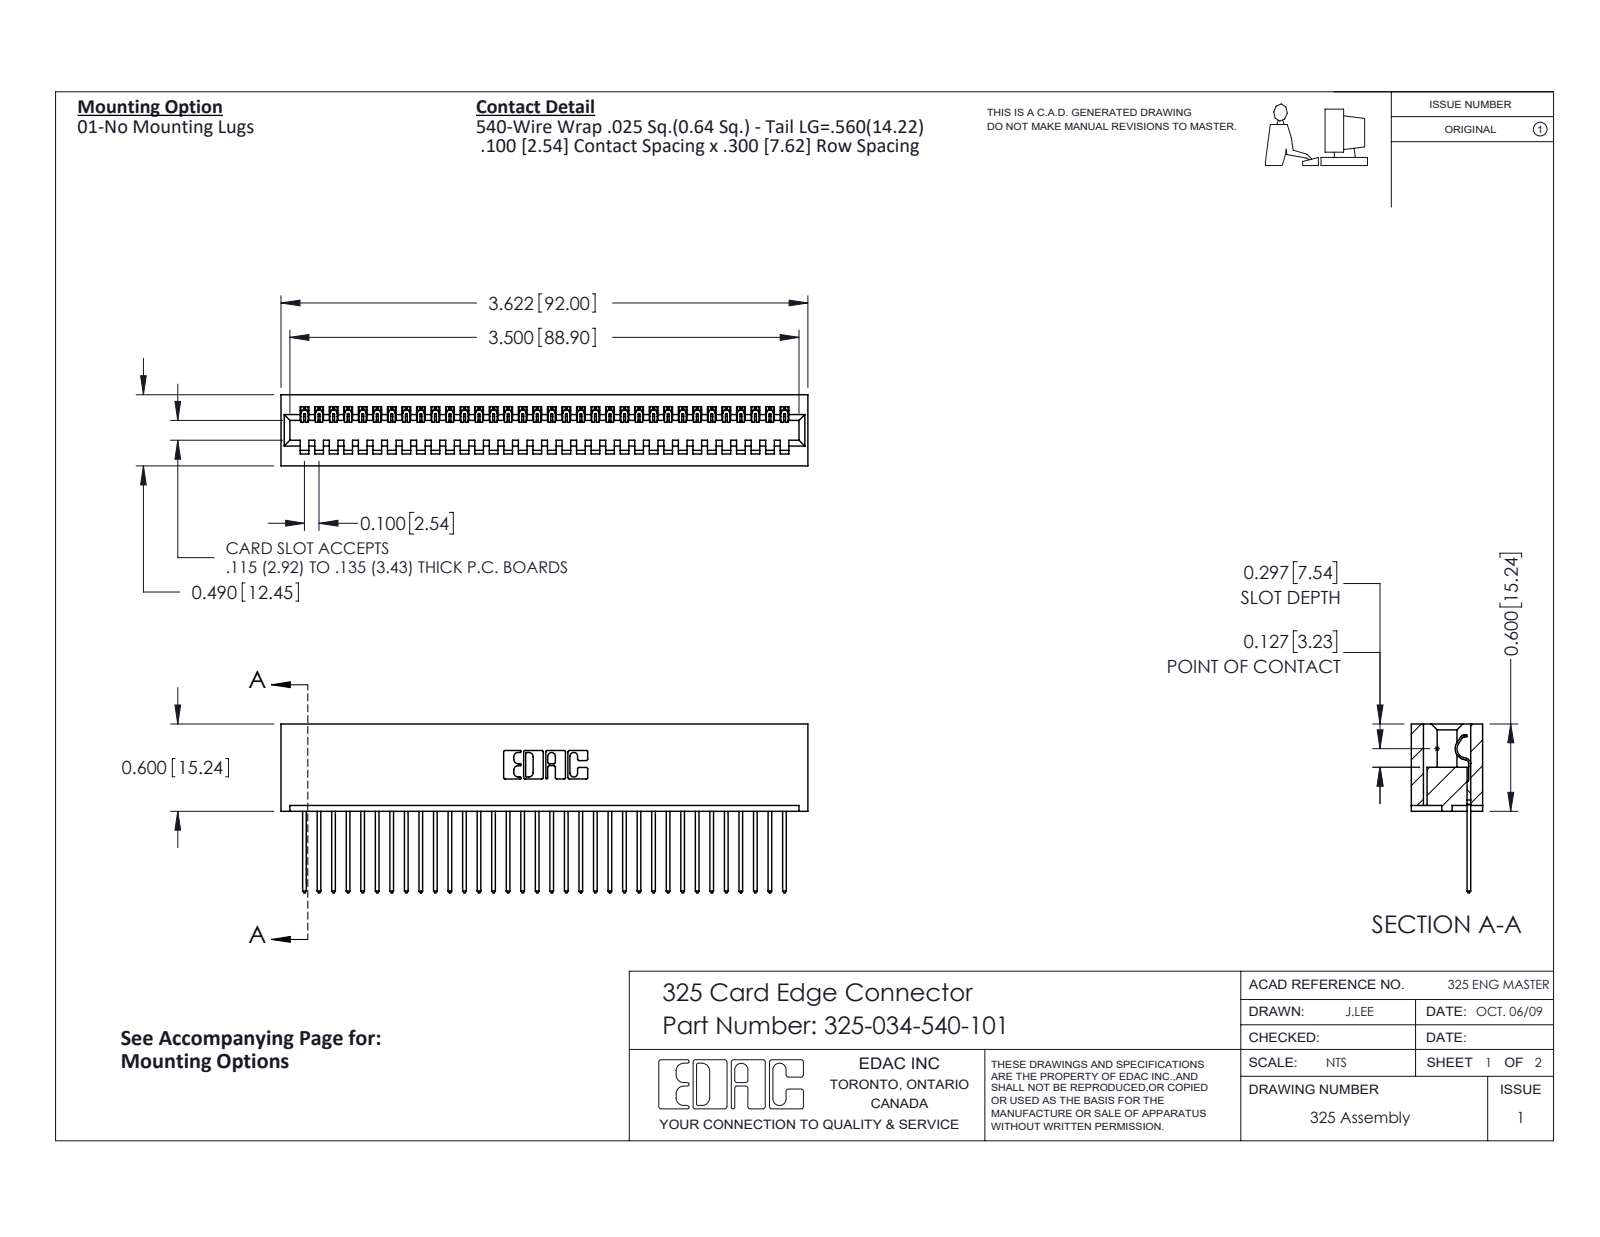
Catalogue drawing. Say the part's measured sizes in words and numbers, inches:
The part is named "325-292-001_325-293-140; 325 Part_Lugless; 325-034-540-101". Its 3-D file was written by "SolidWorks 2016 (CONFIG_CONTROL_DESIGN)". It is 35 solids with 2078 faces: 1494 planar, 584 cylindrical and 0 other. Overall it measures 3.622 by 1.16 by 0.49 inches. Its volume is 0.747 cubic inches and its surface area 21.79 square inches. Partial cylindrical surfaces (rounded edges, fillets, slot ends): 68 of radius 0.006, 68 of radius 0.01, 22 of radius 0.01, 6 of radius 0.007, 6 of radius 0.031, 3 of radius 0.026, 1 of radius 0.014, 1 of radius 0.022. The main face-to-face distances are 0.083, 0.407, 0.3, 0.49, 0.107, 0.383, 0.025, 0.325, 0.1, 0.56.
